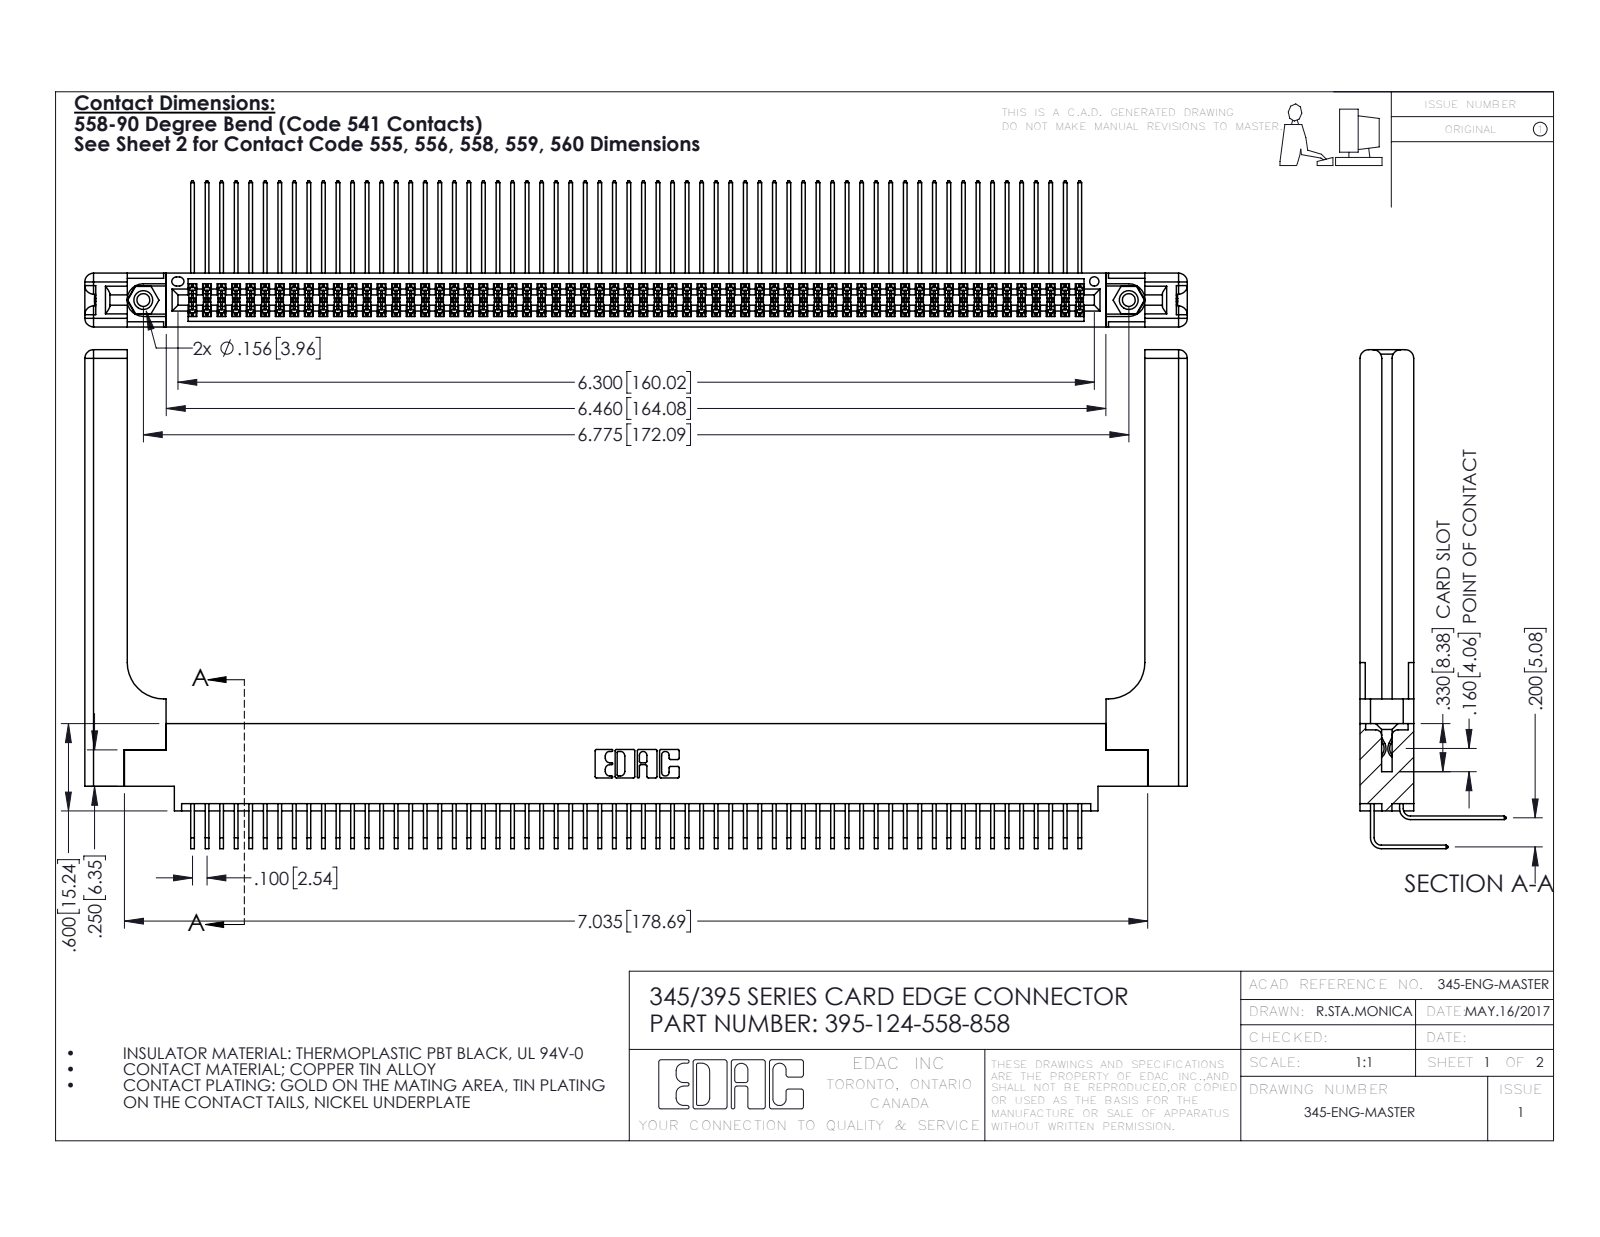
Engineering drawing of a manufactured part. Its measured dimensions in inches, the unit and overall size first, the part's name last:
Units: inches
Overall size (bounding box): 7.579 × 3.429 × 1.005
Round holes (diameter × count): ⌀0.089 ×2, ⌀0.125 ×2, ⌀0.156 ×2, ⌀0.064 ×1
Round bosses / shafts (diameter × count): ⌀0.155 ×2
Partial cylindrical surfaces — rounded edges, fillets, slot ends (radius × count): R0.006 ×187, R0.01 ×22, R0.06 ×16, R0.007 ×6, R0.031 ×6, R0.026 ×3, R0.014 ×2, R0.019 ×2
Main face-to-face distances: 0.072, 0.298, 0.37, 0.2, 0.098, 0.272, 0.025, 0.225, 0.175, 0.025
Hole centre spacings: 0.27, 6.539, 6.775
Volume: 1.706 in³ · Surface area: 58.53 in²
Bodies: 129 solids, 6834 faces (4572 planar, 2202 cylindrical, 60 other)
Part name (STEP PRODUCT): 345-250-001_345-250-001-102; 345 Part_0.170 Offset - 0.156 Dia-TH; 395-124-558-858; 345-292-001_558 559 Tail - 1 (+2 more)
STEP written by: SolidWorks 2016 (CONFIG_CONTROL_DESIGN)
